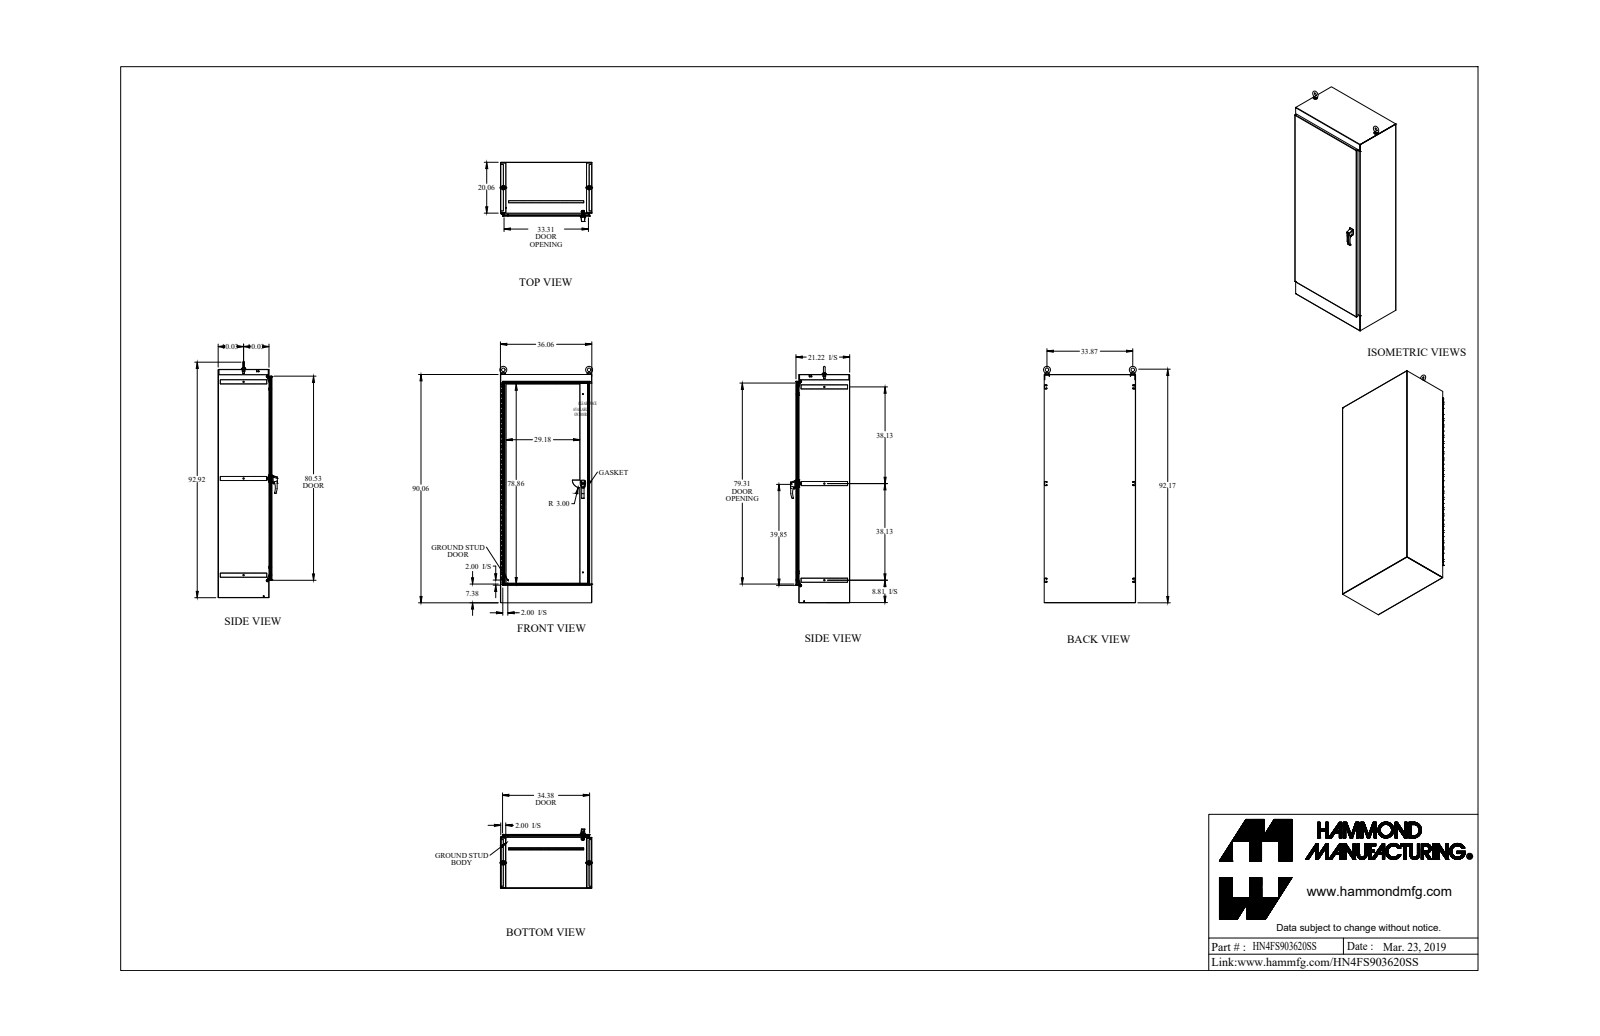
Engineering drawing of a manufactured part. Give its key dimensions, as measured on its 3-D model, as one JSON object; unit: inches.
{"part_name": "HN4FS903620SS", "step_written_by": "SolidWorks 2018 (AUTOMOTIVE_DESIGN)", "units": "inches", "bodies": {"solids": 54, "faces": 2048, "planar": 934, "cylindrical": 949, "other": 165}, "overall_size": [93.489, 36.604, 23.362], "volume_in3": 1292, "surface_area_in2": 27259, "round_holes": [[0.304, 13], [0.35, 7], [0.5, 3], [0.25, 2], [0.257, 2], [0.28, 2], [0.281, 2], [0.313, 2], [0.39, 2], [0.413, 2], [0.527, 2], [0.625, 2]], "round_bosses_or_shafts": [[1.75, 2], [1.5, 2], [1.25, 2], [1, 2], [0.75, 2], [0.738, 2], [0.63, 2], [0.625, 2]], "partial_cylinders_radius": [[0.043, 42], [0.138, 36], [0.5, 23], [0.125, 22], [0.018, 16], [0.06, 15], [0.048, 14], [0.143, 14]], "face_to_face_distances": [0.095, 21.152, 35.965, 21.057, 21.247, 35.87, 36.06, 89.965, 19.965, 1.187], "hole_center_spacings": [6, 12, 18, 24, 30, 36, 42, 48]}
